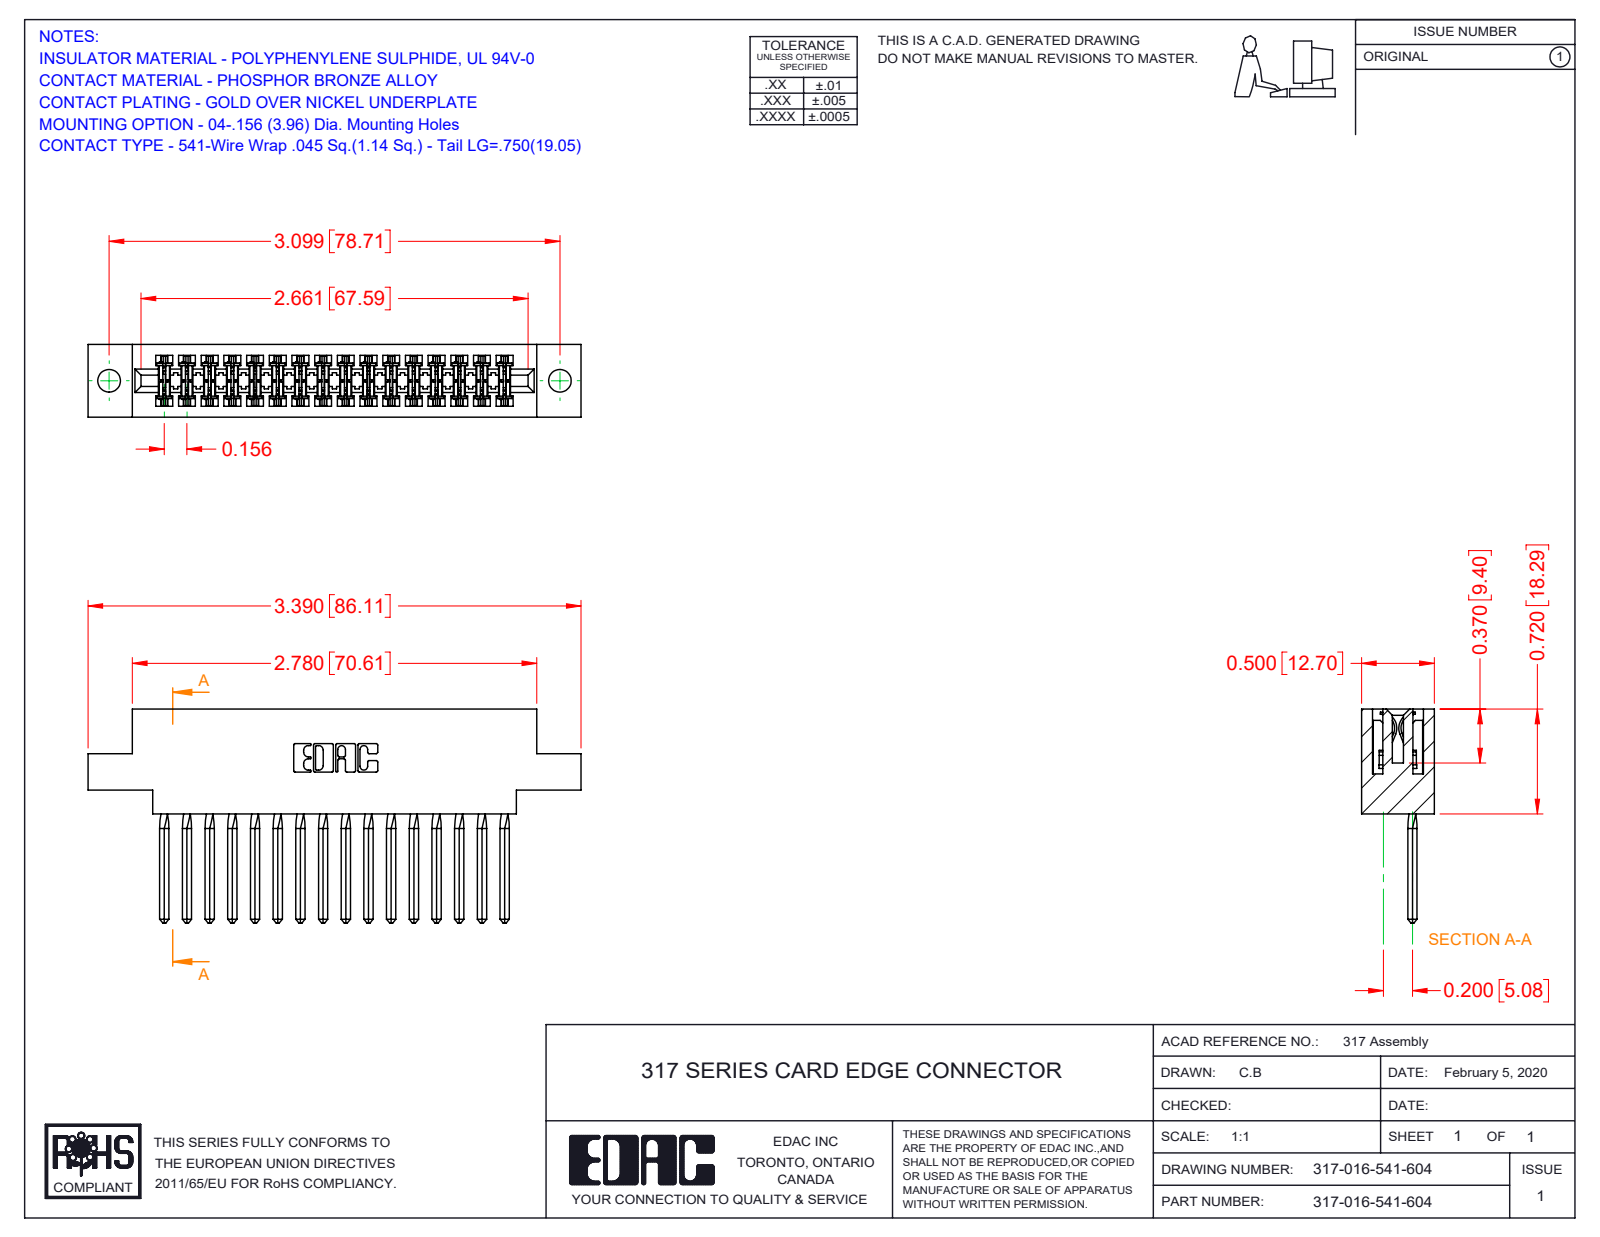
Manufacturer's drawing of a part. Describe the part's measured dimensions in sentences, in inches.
The part is named "317-016-541-604; 317-290-002_541; 317 Part_.156 Dia - TH". Its 3-D file was written by "SolidWorks 2016 (CONFIG_CONTROL_DESIGN)". It is 17 solids with 2534 faces: 2042 planar, 428 cylindrical and 64 other. Overall it measures 3.39 by 1.47 by 0.5 inches. Its volume is 0.798 cubic inches and its surface area 27.01 square inches. Round holes: 2 of diameter 0.156. Partial cylindrical surfaces (rounded edges, fillets, slot ends): 32 of radius 0.015, 22 of radius 0.01, 6 of radius 0.007, 6 of radius 0.031, 3 of radius 0.026, 2 of radius 0.095, 2 of radius 0.1, 2 of radius 0.11. The main face-to-face distances are 0.5, 0.075, 0.425, 0.11, 0.35, 0.22, 0.195, 0.065, 0.72, 0.772. The hole center spacings are 3.099.
